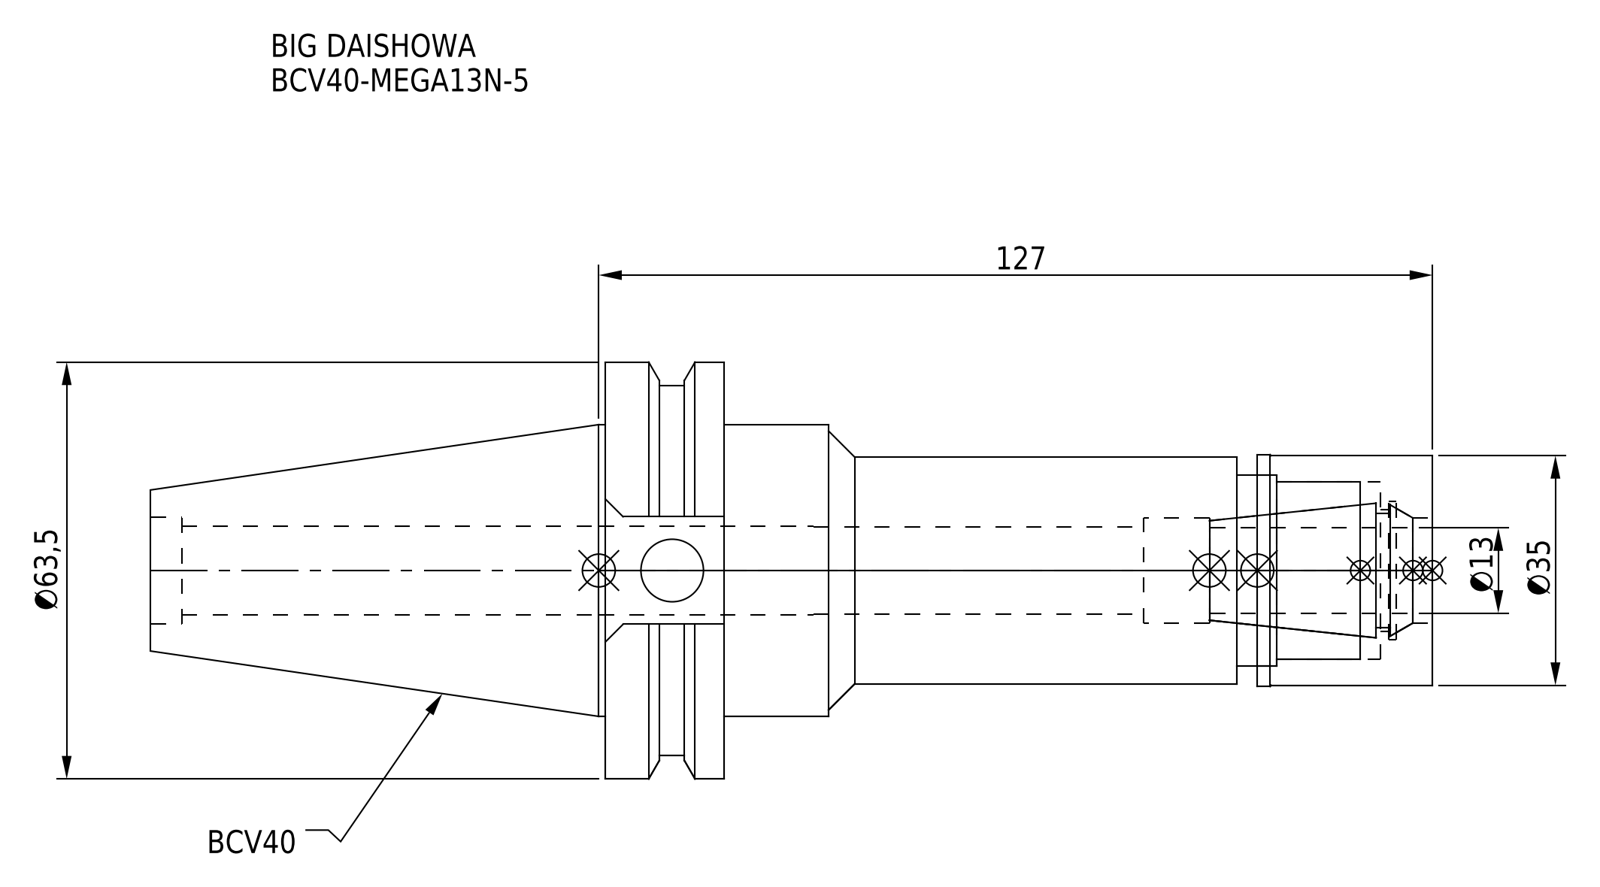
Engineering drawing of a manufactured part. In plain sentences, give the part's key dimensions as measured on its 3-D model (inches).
The part is named "BCV40-MEGA13N-5_1.stp; MGN13_1.stp; BCV40-MEGA13N-5; BCV40-MEGA13N-5-130-FreeParts (+3 more)". Its 3-D file was written by "SolidWorks 2019 (CONFIG_CONTROL_DESIGN)". It is 2 solids with 91 faces: 33 planar, 44 cylindrical and 14 other. Overall it measures 7.687 by 2.5 by 2.415 inches. Its volume is 11.91 cubic inches and its surface area 64.84 square inches. Round holes: 1 of diameter 0.375, 1 of diameter 0.524, 1 of diameter 0.531, 1 of diameter 0.535, 1 of diameter 0.63, 1 of diameter 0.643, 1 of diameter 0.728, 1 of diameter 0.827, 1 of diameter 1.063, 1 of diameter 1.142. Round bosses or shafts: 1 of diameter 2.5, 1 of diameter 2.219, 1 of diameter 1.75, 1 of diameter 1.39, 1 of diameter 1.378, 1 of diameter 1.358. The main face-to-face distances are 0.711, 4.25, 4.961, 1.051, 3.199, 3.909, 0.736, 0.315, 3.935, 4.646.
